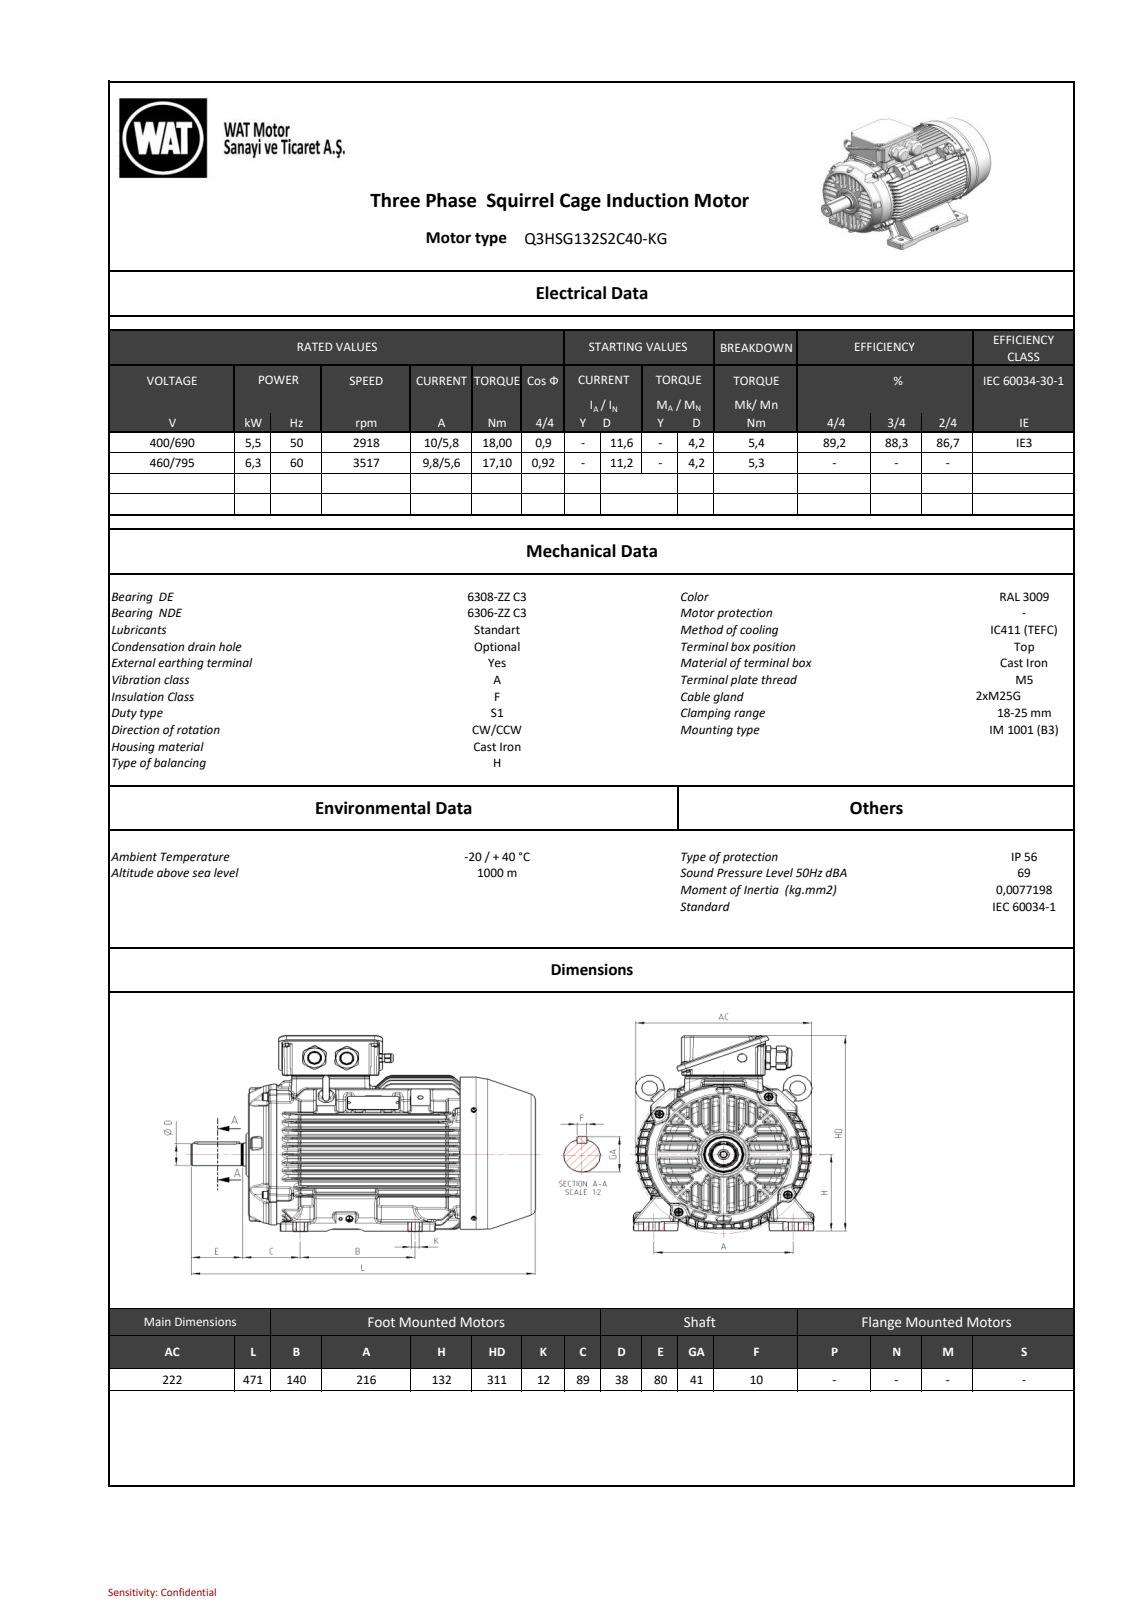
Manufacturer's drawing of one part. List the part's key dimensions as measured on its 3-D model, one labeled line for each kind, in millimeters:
Part name (STEP PRODUCT): C90118903D63mcju
STEP written by: SIEMENS PLM Software NX 11.0 (AUTOMOTIVE_DESIGN)
Units: millimetres
Bodies: 0 solids, 5671 faces (992 planar, 1550 cylindrical, 3129 other)
Overall size (bounding box): 471 × 311.13 × 275
Round holes (diameter × count): ⌀5 ×9, ⌀2.5 ×2, ⌀6.8 ×2, ⌀10 ×2, ⌀17.2 ×2, ⌀6.3 ×1, ⌀8 ×1, ⌀10.2 ×1, ⌀13 ×1, ⌀58.4 ×1, ⌀58.6 ×1, ⌀212 ×1
Round bosses / shafts (diameter × count): ⌀12 ×4, ⌀10 ×4, ⌀8.65 ×4, ⌀8 ×4, ⌀4 ×4, ⌀27.7 ×2, ⌀25.25 ×2, ⌀20 ×2
Partial cylindrical surfaces — rounded edges, fillets, slot ends (radius × count): R4 ×320, R0.5 ×128, R3 ×113, R1.5 ×96, R2 ×45, R1 ×40, R1.8 ×36, R0.25 ×28
Main face-to-face distances: 13.1, 13.18, 26.28, 39.54, 26.44, 13.26, 90.54, 52.86, 39.76, 26.58
Hole centre spacings: 97, 137.18, 33.69, 111.28, 158.92, 191.06, 194.01, 27.5
